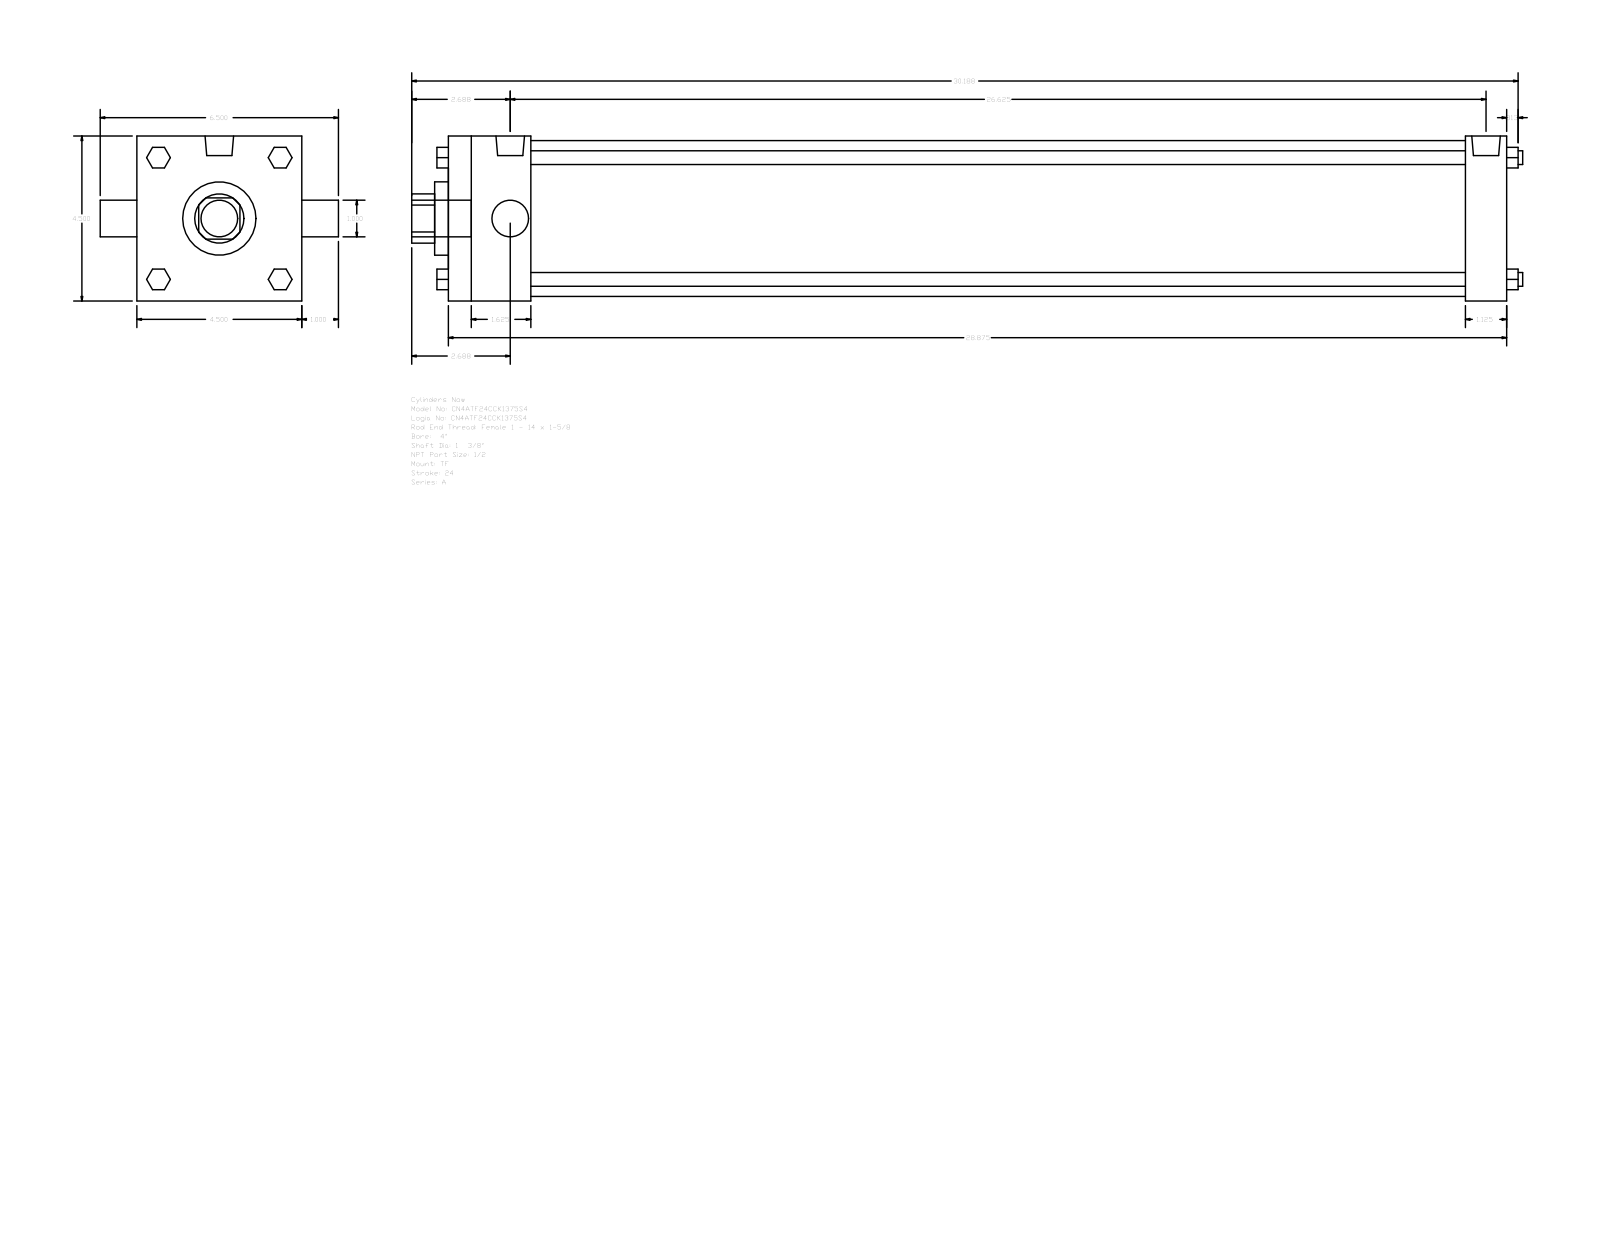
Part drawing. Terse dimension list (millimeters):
name: A_TF__0400_1.375
written by: GSSL Pune (CONFIG_CONTROL_DESIGN)
unit: mm
bodies: 0 solids, 120 faces (92 planar, 28 cylindrical, 0 other)
size: 769.94 × 165.1 × 114.3
holes: 1× ⌀25.4, 1× ⌀34.92, 1× ⌀50.8, 1× ⌀107.95
bosses: 4× ⌀9.53, 3× ⌀8.73, 2× ⌀19.77, 1× ⌀25.4
rounds: 1× R17.06
face distances: 114.3, 733.43, 28.58, 704.85, 57.15, 647.7, 676.28, 14.29, 25.4, 9.52
